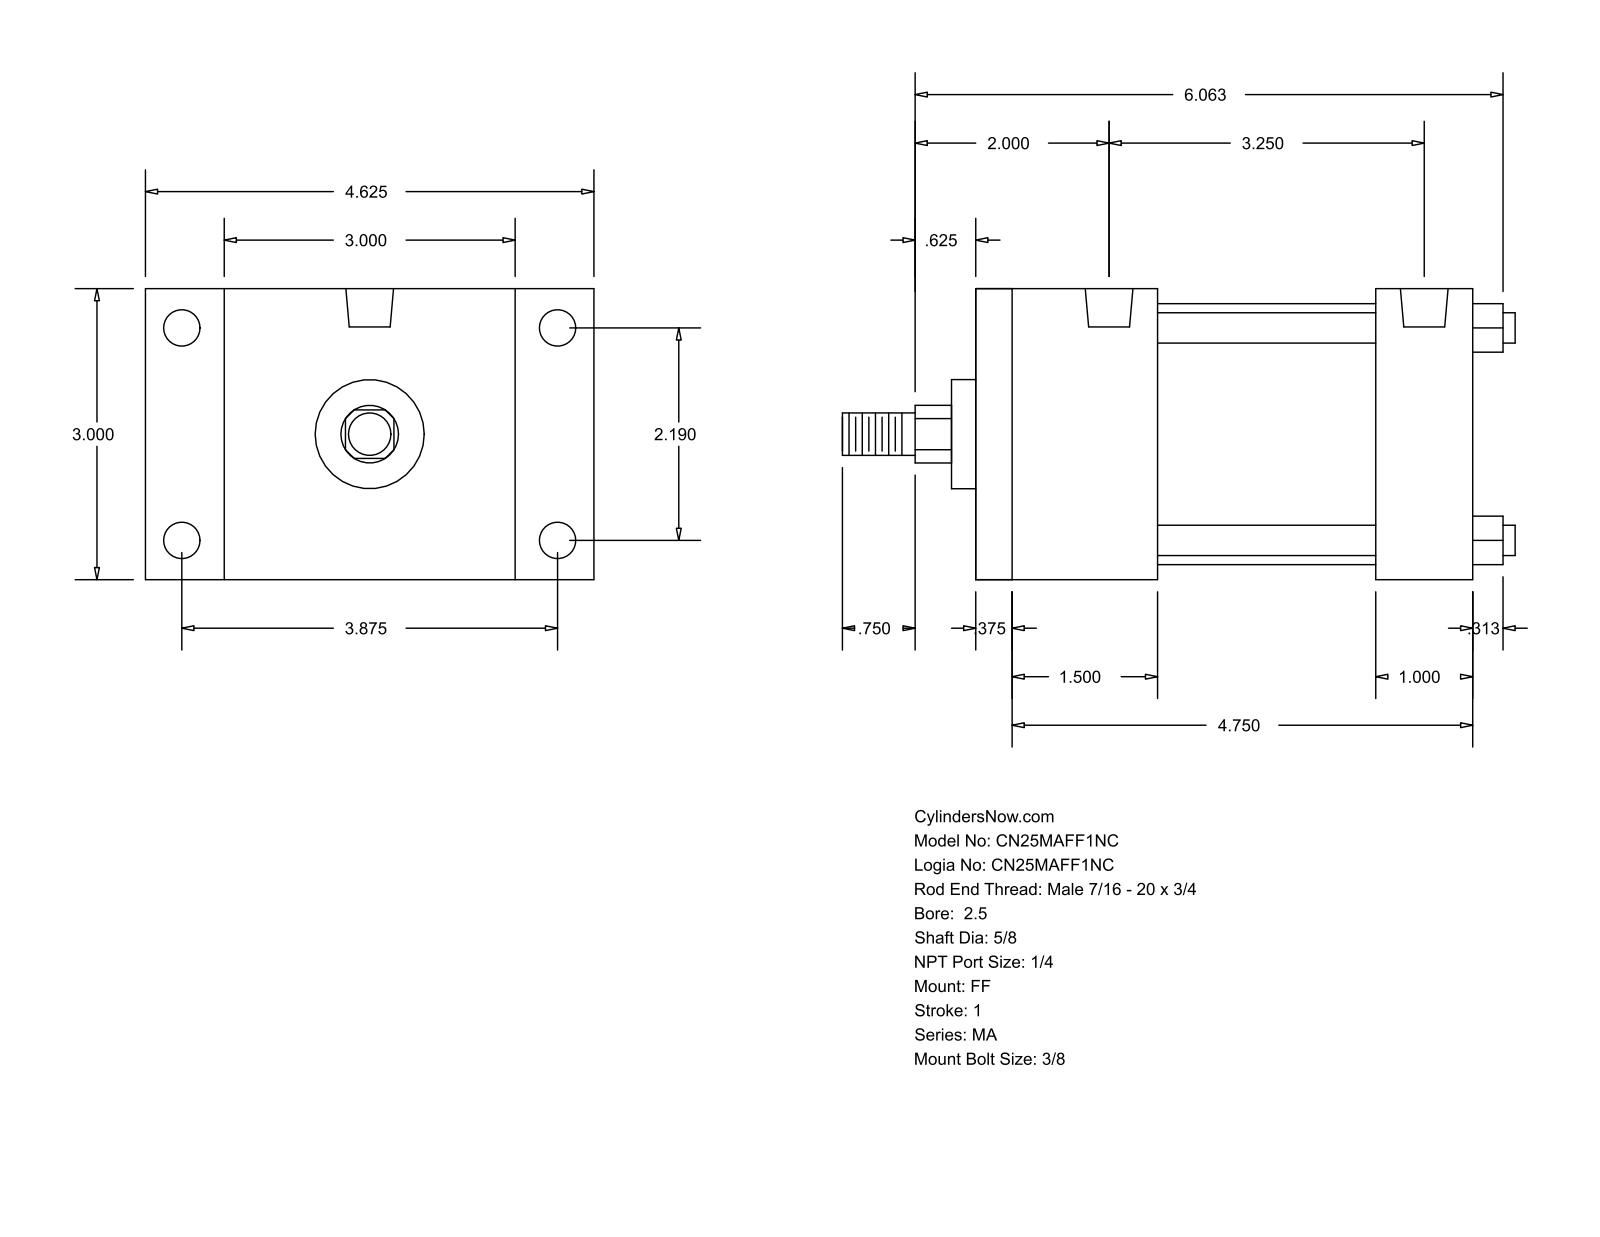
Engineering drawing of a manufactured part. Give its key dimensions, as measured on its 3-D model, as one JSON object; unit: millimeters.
{"part_name": "MA_FF__0250_0.625", "step_written_by": "GSSL Pune (CONFIG_CONTROL_DESIGN)", "units": "millimeters", "bodies": {"solids": 0, "faces": 92, "planar": 64, "cylindrical": 28, "other": 0}, "overall_size": [176.21, 117.47, 76.2], "round_holes": [[7.94, 4], [9.53, 4], [12.49, 2]], "round_bosses_or_shafts": [[7.94, 4], [68.33, 1], [28.57, 1], [15.88, 1], [11.11, 1]], "partial_cylinders_radius": [[7.54, 1]], "face_to_face_distances": [76.2, 130.17, 120.65, 9.52, 25.4, 82.55, 57.15, 47.62, 104.77, 38.1], "hole_center_spacings": [55.62, 82.55, 98.42, 113.05]}
